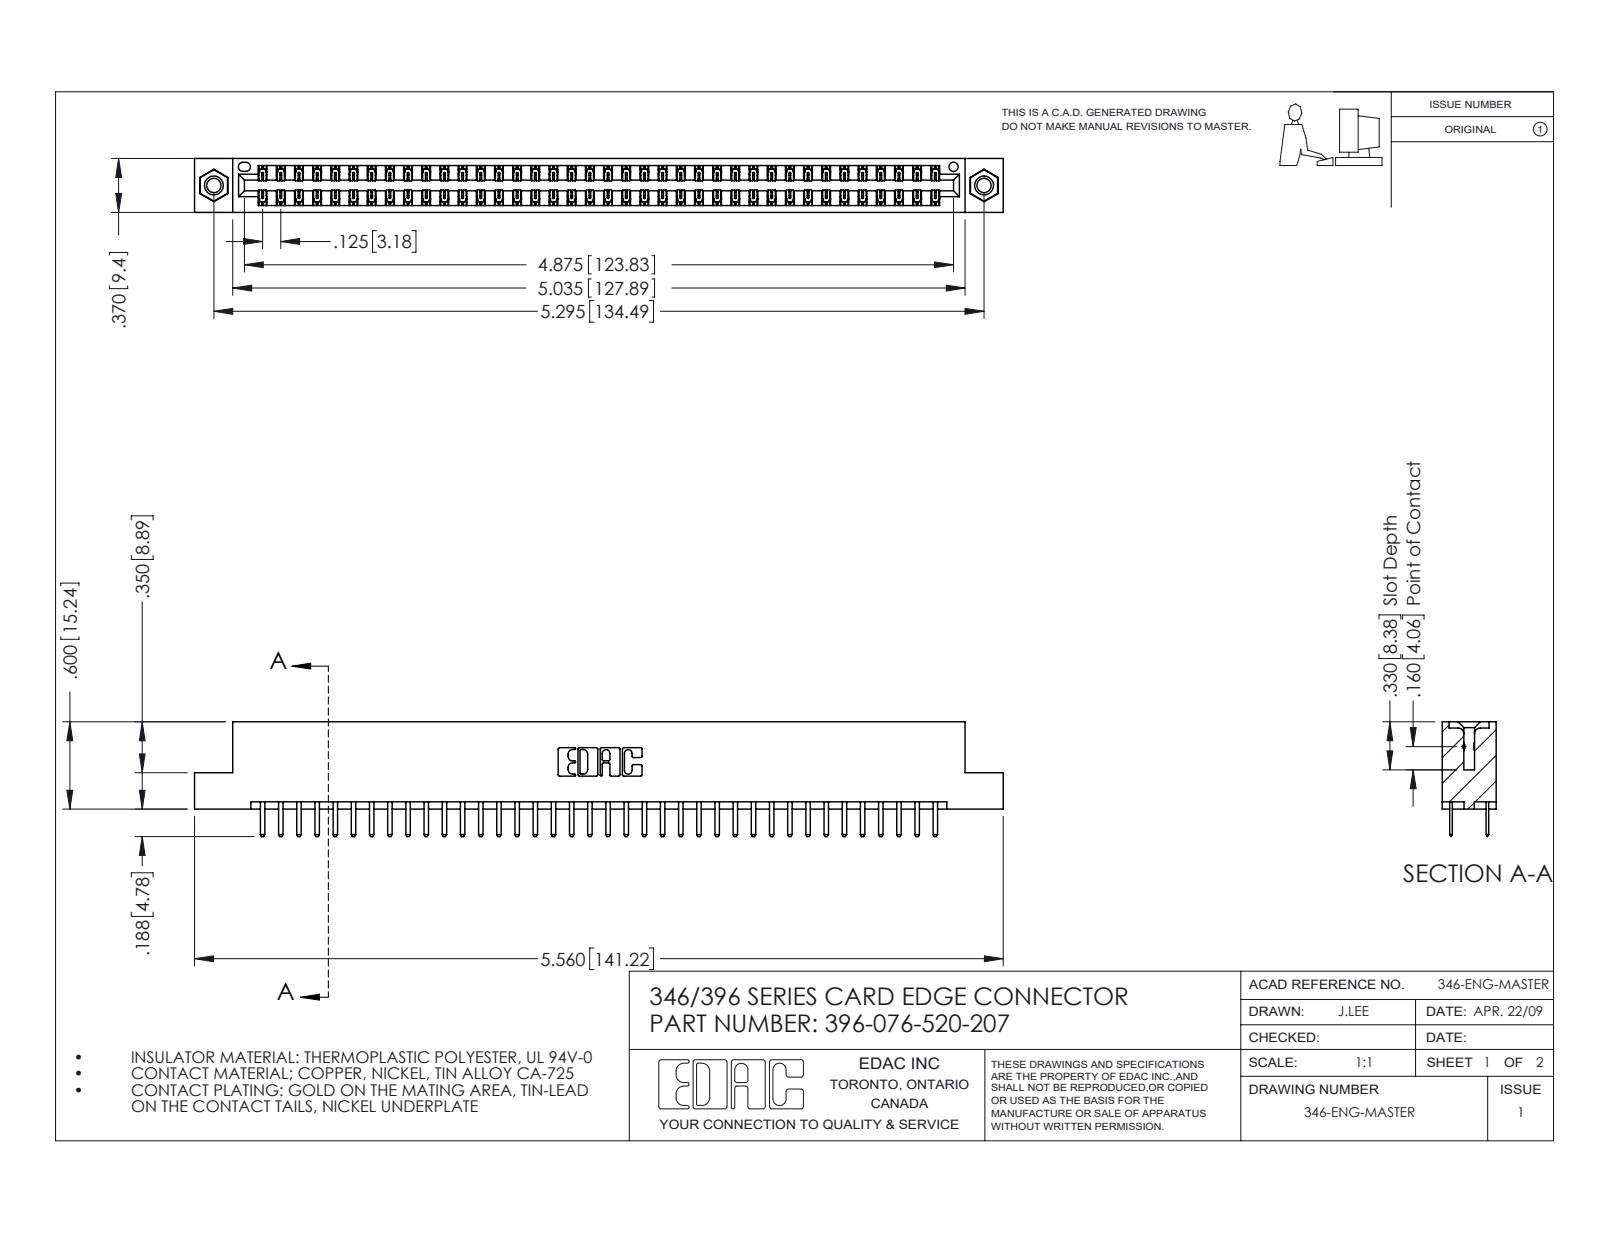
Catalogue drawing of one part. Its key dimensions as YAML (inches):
part_name: "346 Part_Flush Mounting Lugs - 0.156 Dia-TI; 345-250-001_345-250-005-103; 396-076-520-207; 345-292-001_345-293-120"
step_written_by: "SolidWorks 2016 (CONFIG_CONTROL_DESIGN)"
units: inches
bodies: {solids: 79, faces: 4438, planar: 2920, cylindrical: 1502, other: 16}
overall_size: [5.56, 0.788, 0.37]
volume: 0.836
surface_area: 29.01
round_holes:
  - {diameter: 0.098, count: 2}
  - {diameter: 0.125, count: 2}
  - {diameter: 0.156, count: 2}
  - {diameter: 0.064, count: 1}
round_bosses_or_shafts:
  - {diameter: 0.155, count: 2}
partial_cylinders:
  - {radius: 0.006, count: 114}
  - {radius: 0.01, count: 80}
  - {radius: 0.01, count: 22}
  - {radius: 0.007, count: 6}
  - {radius: 0.031, count: 6}
  - {radius: 0.026, count: 3}
  - {radius: 0.014, count: 2}
  - {radius: 0.022, count: 2}
face_to_face_distances: [0.048, 0.322, 0.25, 0.37, 0.275, 0.072, 0.298, 0.025, 0.148, 0.222]
hole_center_spacings: [0.246, 5.086, 5.295]
